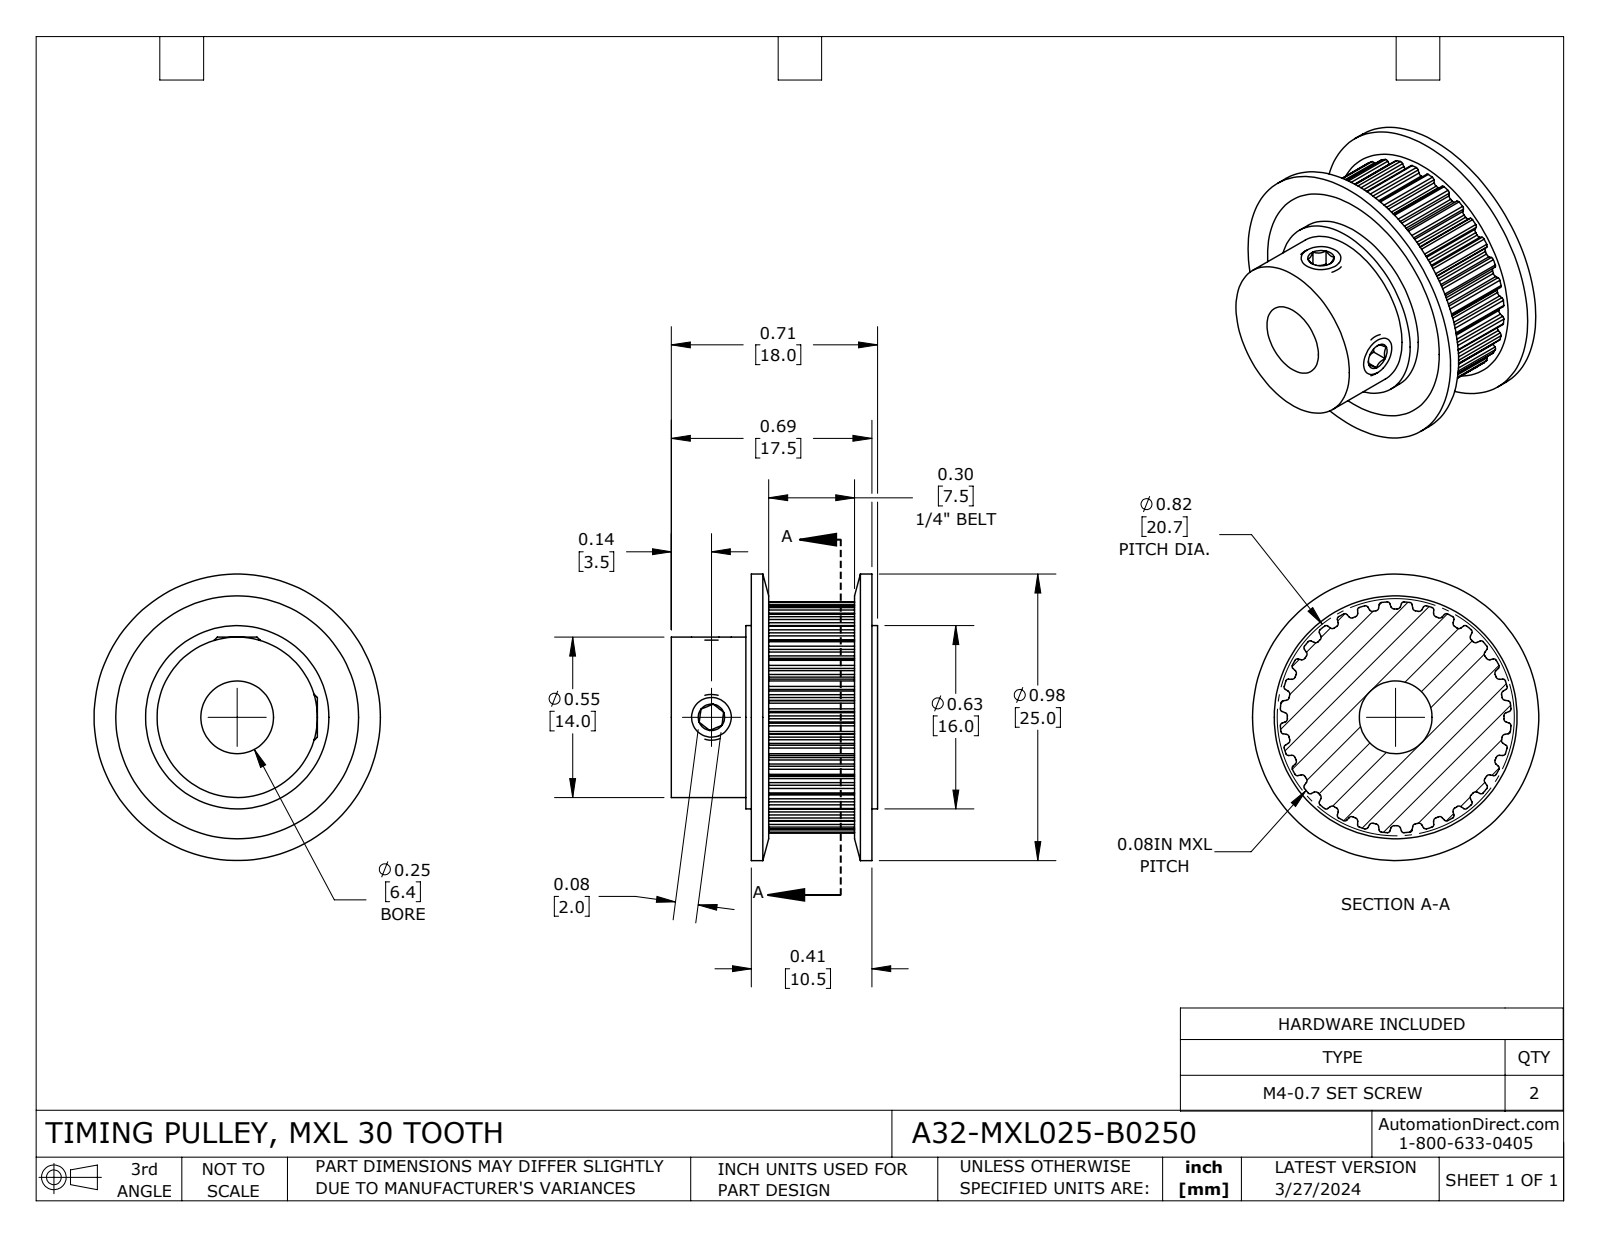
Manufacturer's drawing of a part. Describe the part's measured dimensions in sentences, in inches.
The part is named "A32-MXL025-B0250". Its 3-D file was written by "SolidWorks 2021 (CONFIG_CONTROL_DESIGN)". It is 5 solids with 368 faces: 89 planar, 245 cylindrical and 34 other. Overall it measures 0.984 by 0.984 by 0.709 inches. Its volume is 0.248 cubic inches and its surface area 5.636 square inches. Round holes: 2 of diameter 0.13, 1 of diameter 0.25, 1 of diameter 0.63. Round bosses or shafts: 2 of diameter 0.157, 1 of diameter 0.984, 1 of diameter 0.551. Partial cylindrical surfaces (rounded edges, fillets, slot ends): 64 of radius 0.009, 64 of radius 0.012, 1 of radius 0.372, 1 of radius 0.398. The main face-to-face distances are 0.039, 0.335, 0.295, 0.374, 0.079, 0.413, 0.709, 0.669, 0.63, 0.453.
